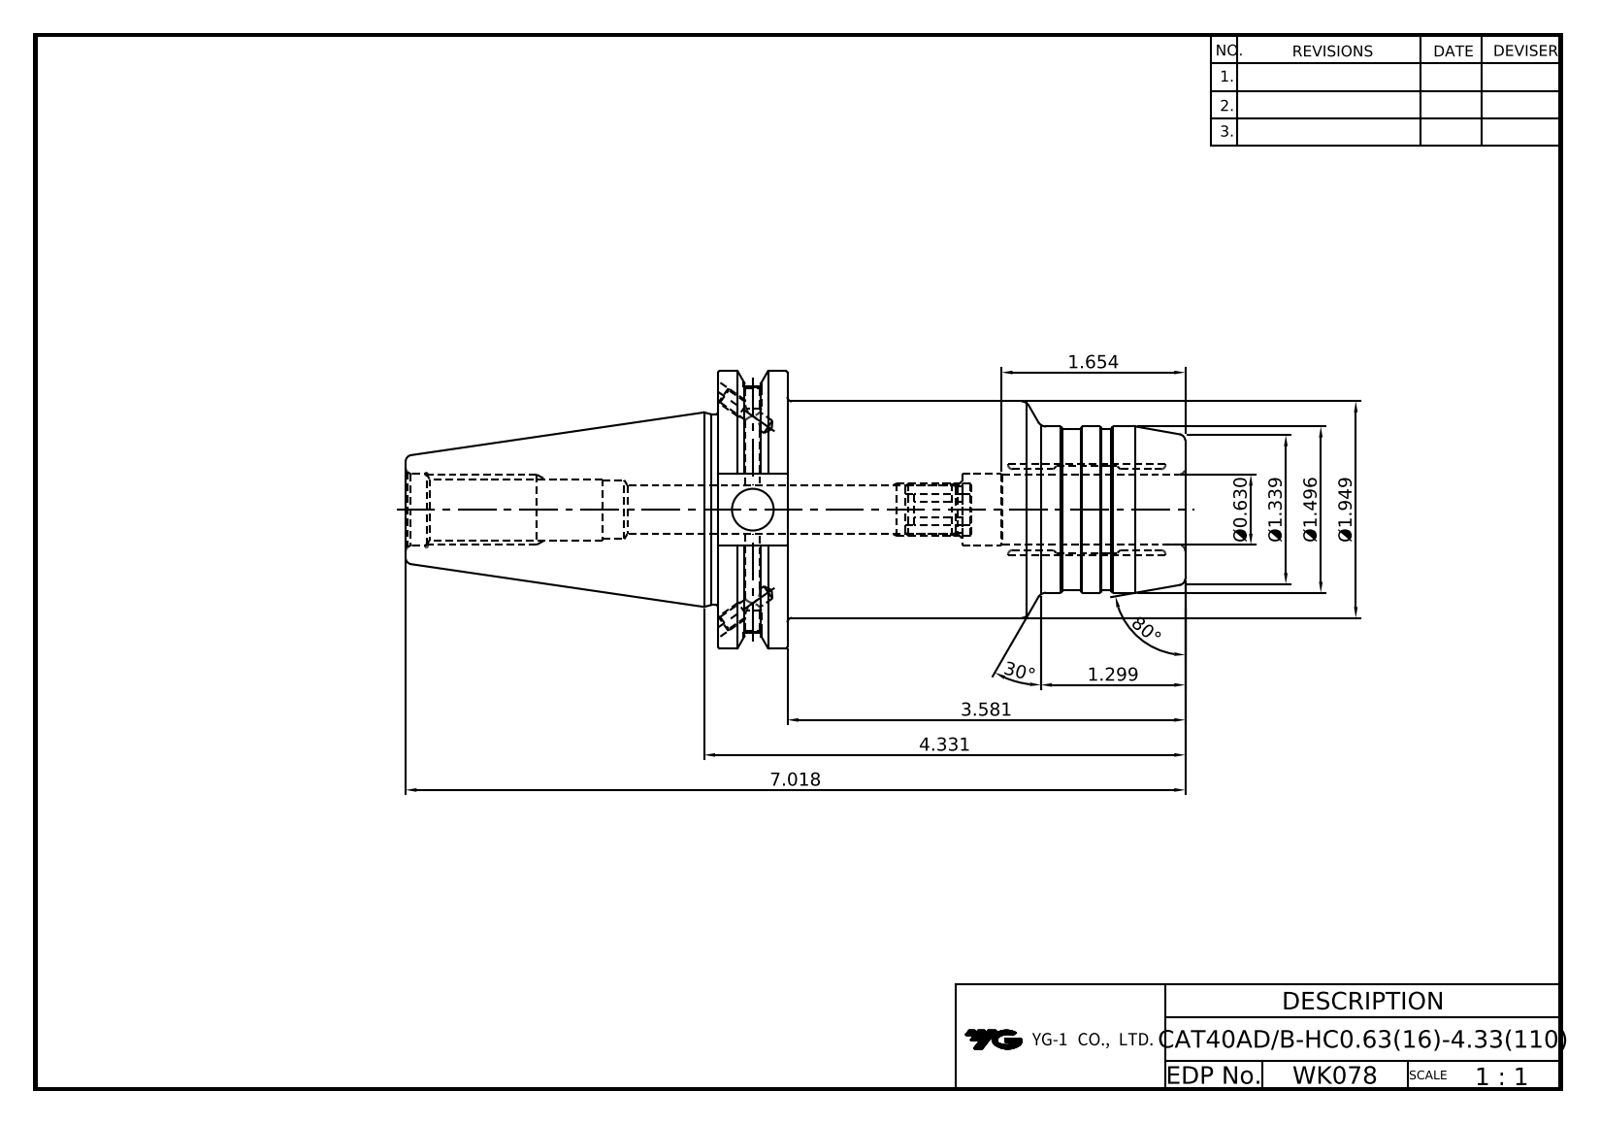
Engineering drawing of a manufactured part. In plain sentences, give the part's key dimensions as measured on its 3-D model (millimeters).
The part is named "LO-CAT40ADB-HC16-110". Its 3-D file was written by "Autodesk Inventor 2020 (AUTOMOTIVE_DESIGN)". It is 1 solid with 106 faces: 34 planar, 35 cylindrical and 37 other. Overall it measures 178.25 by 63.5 by 61.09 millimeters. Its volume is 233 823 cubic millimeters and its surface area 36 750 square millimeters. Round holes: 4 of diameter 3.24, 2 of diameter 4, 2 of diameter 4.2, 1 of diameter 9.53, 1 of diameter 10.92, 1 of diameter 13, 1 of diameter 13.39, 1 of diameter 16, 1 of diameter 16.3, 1 of diameter 16.6. Round bosses or shafts: 1 of diameter 63.5, 1 of diameter 49.5, 1 of diameter 43.6, 1 of diameter 38, 1 of diameter 37. Partial cylindrical surfaces (rounded edges, fillets, slot ends): 1 of radius 8.19, 1 of radius 28.15. The main face-to-face distances are 15.88, 106.83, 90.95, 47.6, 16.38, 71.42, 87.3, 178.25, 127.25, 55.83.
